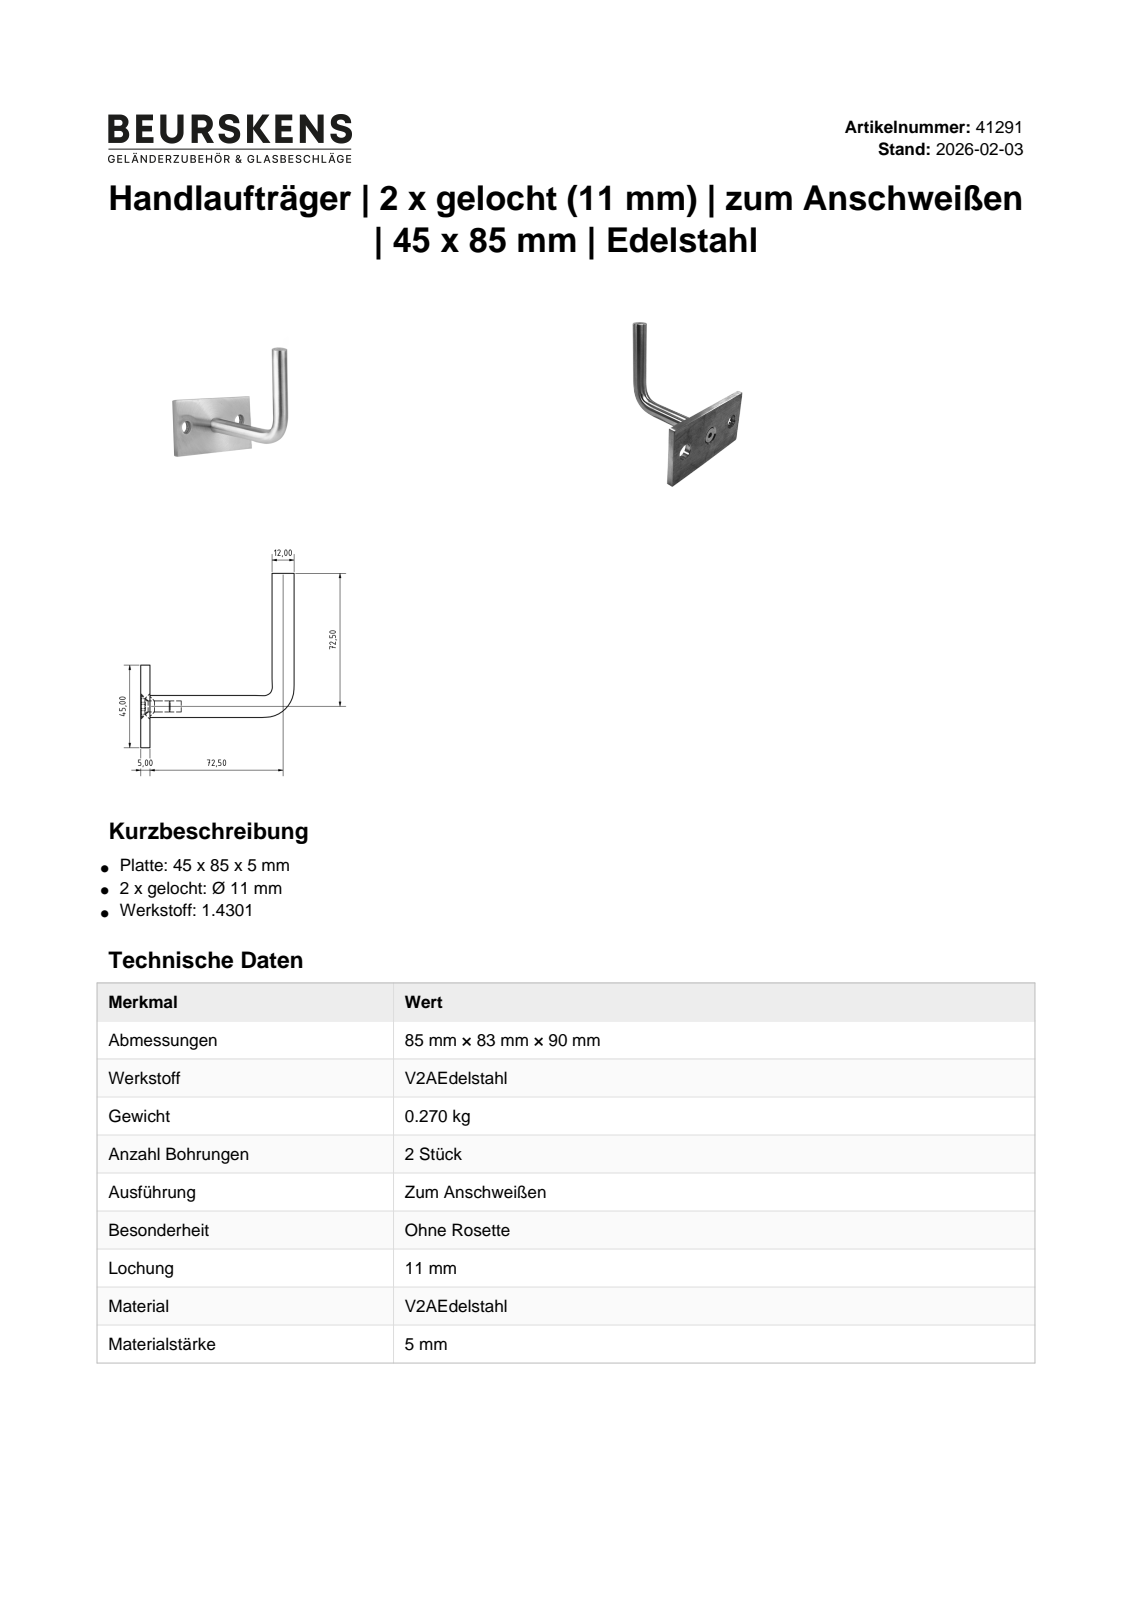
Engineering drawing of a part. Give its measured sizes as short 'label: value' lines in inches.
name: 41291; DIN 7991 - M6x16; 41270; 41285
written by: Autodesk Inventor 2022 (AUTOMOTIVE_DESIGN)
unit: in
bodies: 3 solids, 30 faces (18 planar, 6 cylindrical, 6 other)
size: 3.74 × 3.346 × 3.288
volume: 2.054 in³; area: 23.71 in²
holes: 2× ⌀0.433, 1× ⌀0.236
bosses: 1× ⌀0.472, 1× ⌀0.236
face distances: 0.197, 1.772, 3.346, 1.969, 3.74, 0.866, 0.669, 0.63, 0.157, 0.098
hole spacings: 1.181, 2.362
